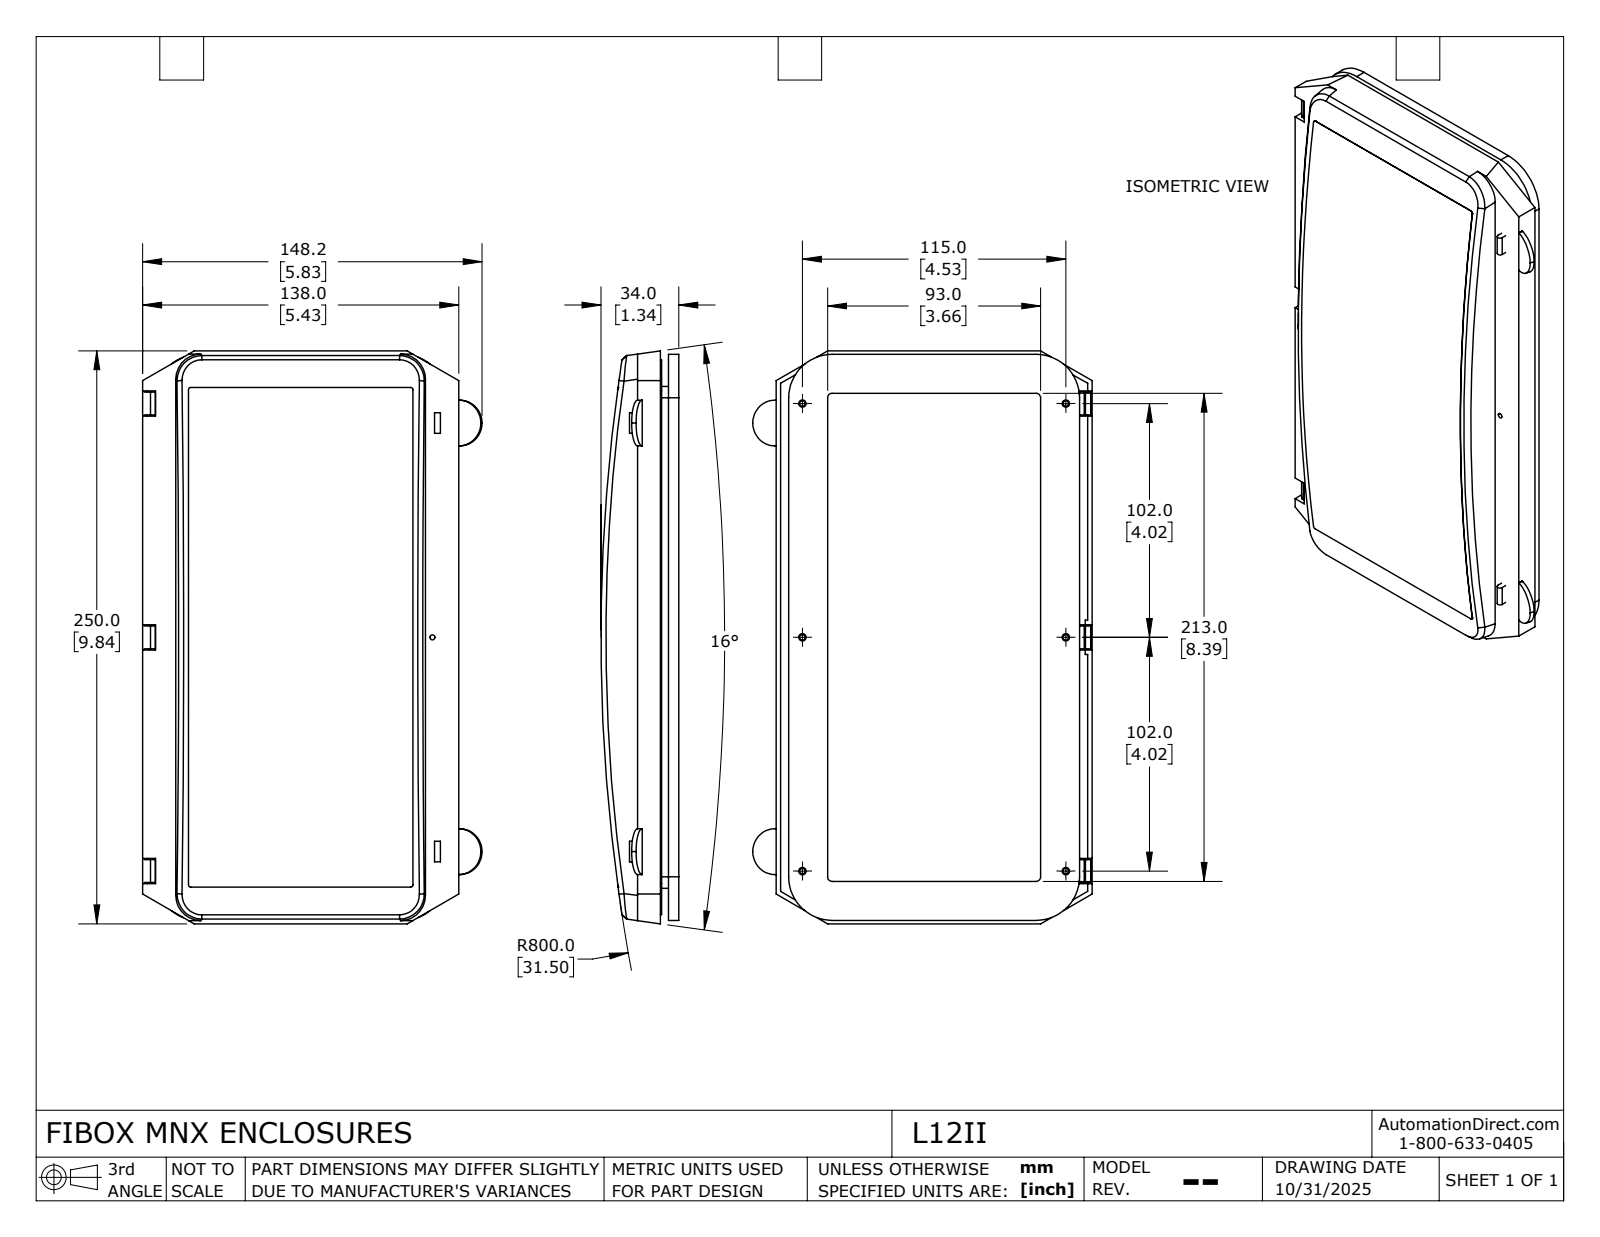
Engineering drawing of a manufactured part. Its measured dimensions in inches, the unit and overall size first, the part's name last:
Units: inches
Overall size (bounding box): 9.843 × 5.834 × 1.339
Round holes (diameter × count): ⌀0.094 ×6, ⌀0.126 ×6, ⌀0.087 ×1
Partial cylindrical surfaces — rounded edges, fillets, slot ends (radius × count): R0.079 ×12, R0.037 ×4, R0.197 ×4, R0.433 ×4, R0.531 ×4, R0.748 ×4, R0.02 ×2, R0.11 ×2
Main face-to-face distances: 0.118, 0.079, 0.453, 0.335, 0.571, 0.177, 0.138, 0.059, 0.295, 0.63
Hole centre spacings: 4.016, 6.052, 4.528, 8.031, 9.22
Volume: 14.6 in³ · Surface area: 238.3 in²
Bodies: 2 solids, 237 faces (135 planar, 84 cylindrical, 18 other)
Part name (STEP PRODUCT): L12II_Default
STEP written by: SolidWorks 2024 (CONFIG_CONTROL_DESIGN)
